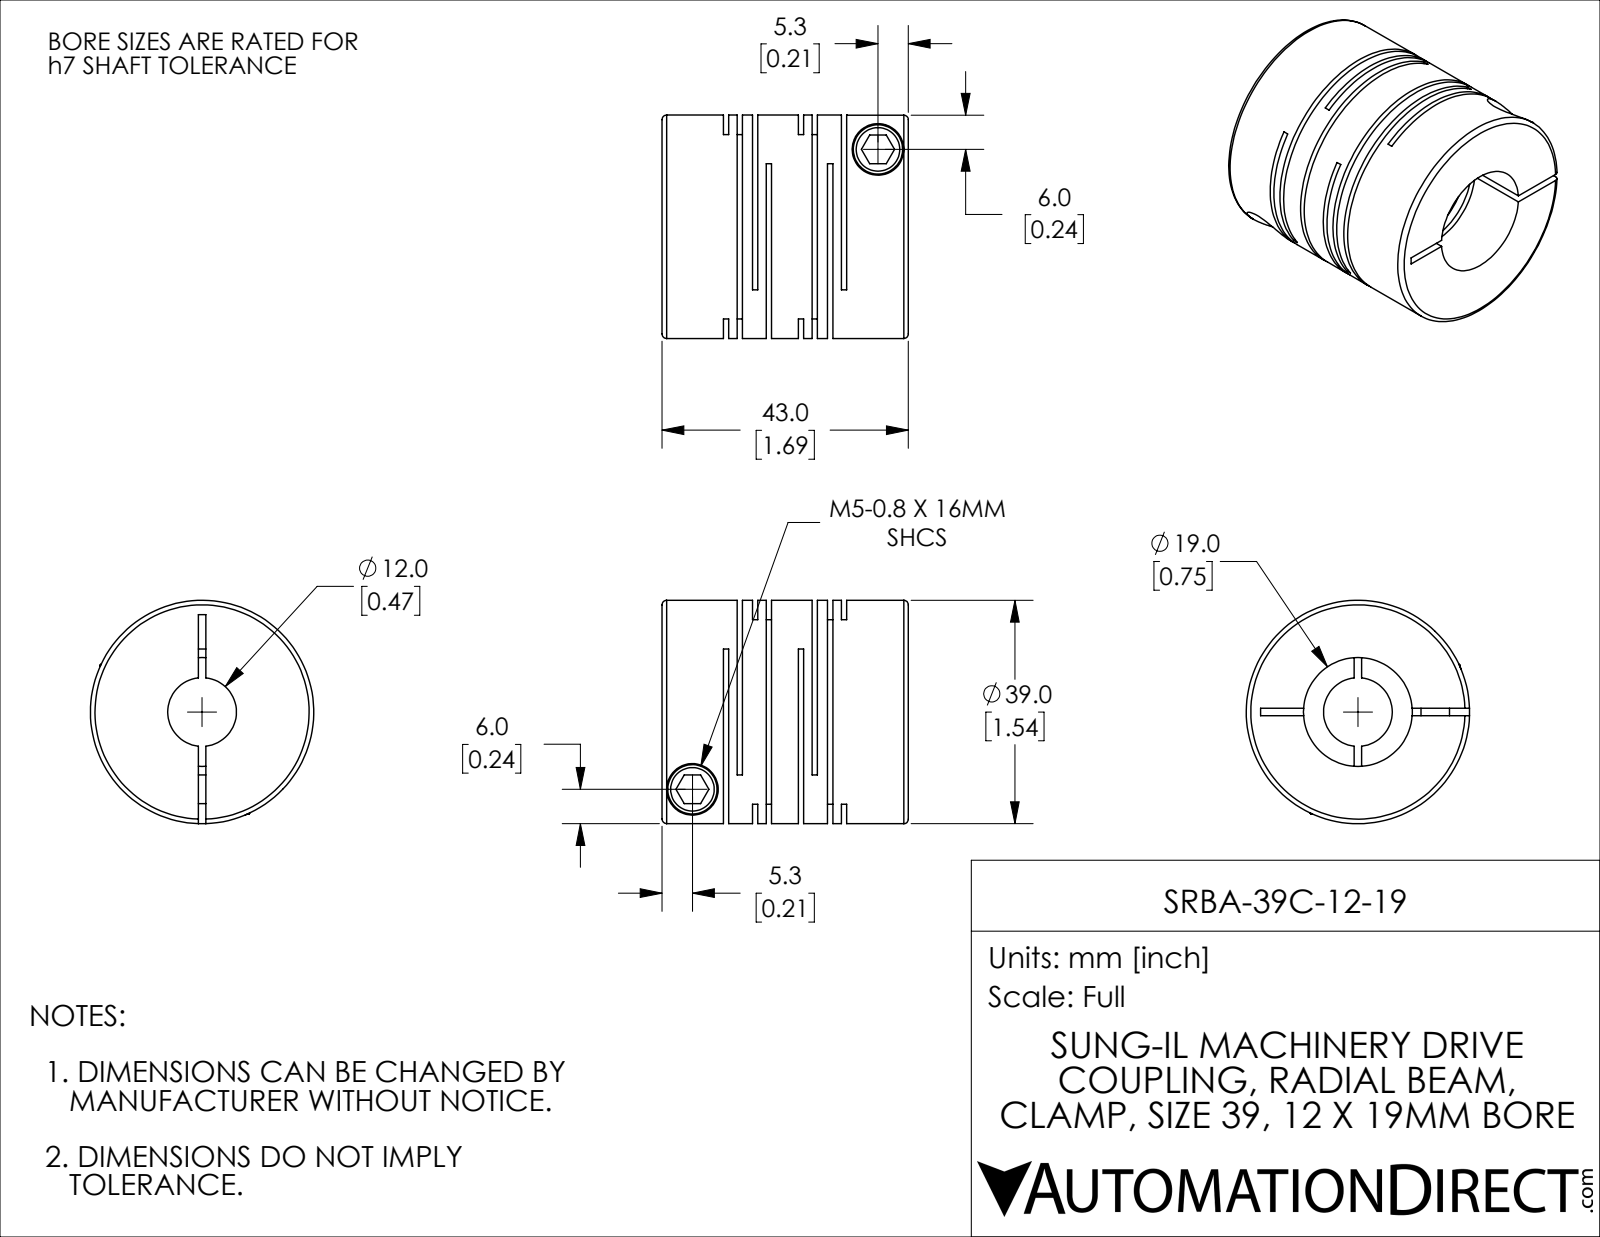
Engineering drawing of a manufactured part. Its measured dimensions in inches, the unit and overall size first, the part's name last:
Units: inches
Overall size (bounding box): 1.693 × 1.535 × 1.535
Round holes (diameter × count): ⌀0.197 ×2, ⌀0.354 ×2, ⌀0.472 ×1, ⌀0.748 ×1
Round bosses / shafts (diameter × count): ⌀0.339 ×2, ⌀1.535 ×1
Main face-to-face distances: 0.516, 0.036, 0.094, 0.201, 0.421, 0.552, 0.717, 0.131, 0.61, 0.058
Volume: 2.088 in³ · Surface area: 33.96 in²
Bodies: 1 solid, 114 faces (60 planar, 42 cylindrical, 12 other)
Part name (STEP PRODUCT): SRBA-39C-12-19
STEP written by: SolidWorks 2021 (CONFIG_CONTROL_DESIGN)
